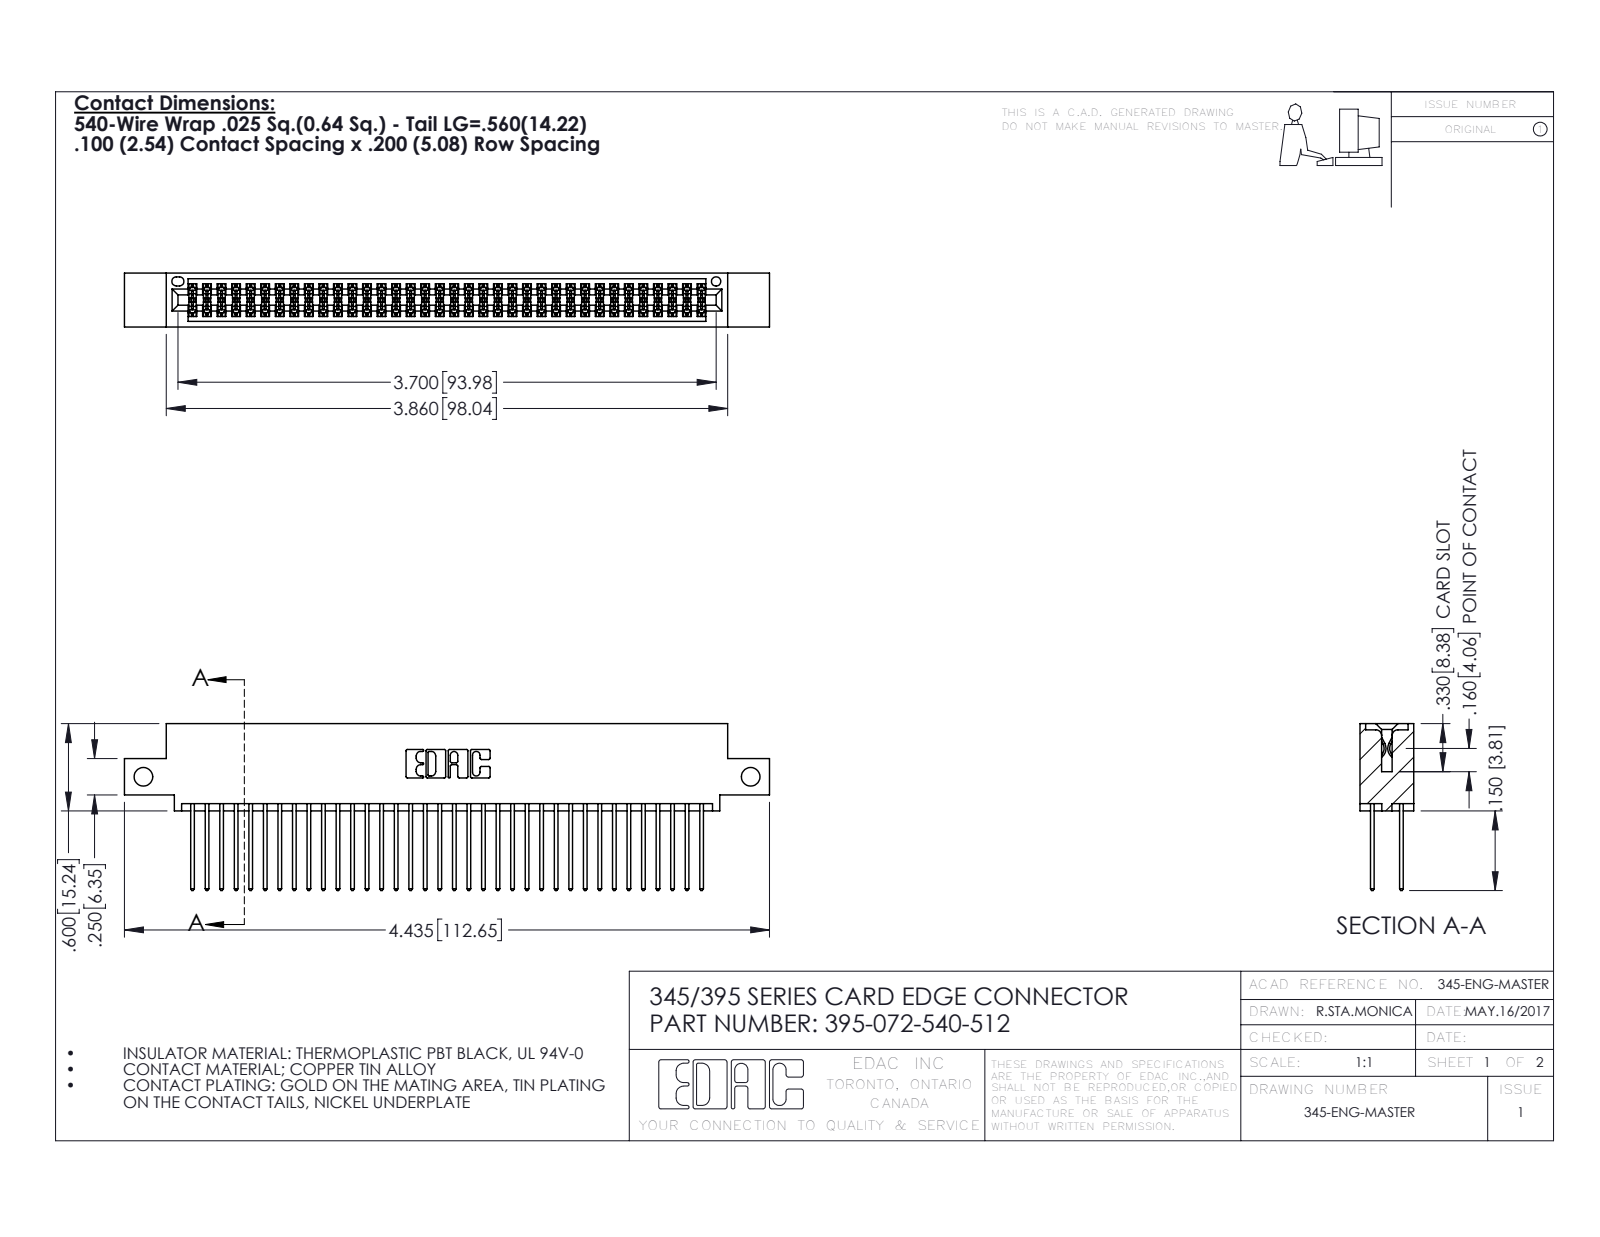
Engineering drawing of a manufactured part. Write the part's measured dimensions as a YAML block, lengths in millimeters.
part_name: "395-072-540-512; 345-292-001_345-293-140; 345 Part_0.110 Offset - Side Mount"
step_written_by: "SolidWorks 2016 (CONFIG_CONTROL_DESIGN)"
units: millimeters
bodies: {solids: 73, faces: 3730, planar: 2460, cylindrical: 1270, other: 0}
overall_size: [112.6, 29.1, 9.4]
volume: 11000
surface_area: 17370
round_holes:
  - {diameter: 3.3, count: 2}
  - {diameter: 1.6, count: 1}
partial_cylinders:
  - {radius: 0.2, count: 108}
  - {radius: 0.3, count: 72}
  - {radius: 0.3, count: 22}
  - {radius: 0.2, count: 6}
  - {radius: 0.8, count: 6}
  - {radius: 0.7, count: 3}
  - {radius: 0.4, count: 2}
  - {radius: 0.5, count: 2}
face_to_face_distances: [7.6, 1.8, 5.1, 2.5, 6.9, 0.6, 9.4, 5.7, 4.4, 3.8]
hole_center_spacings: [106]
